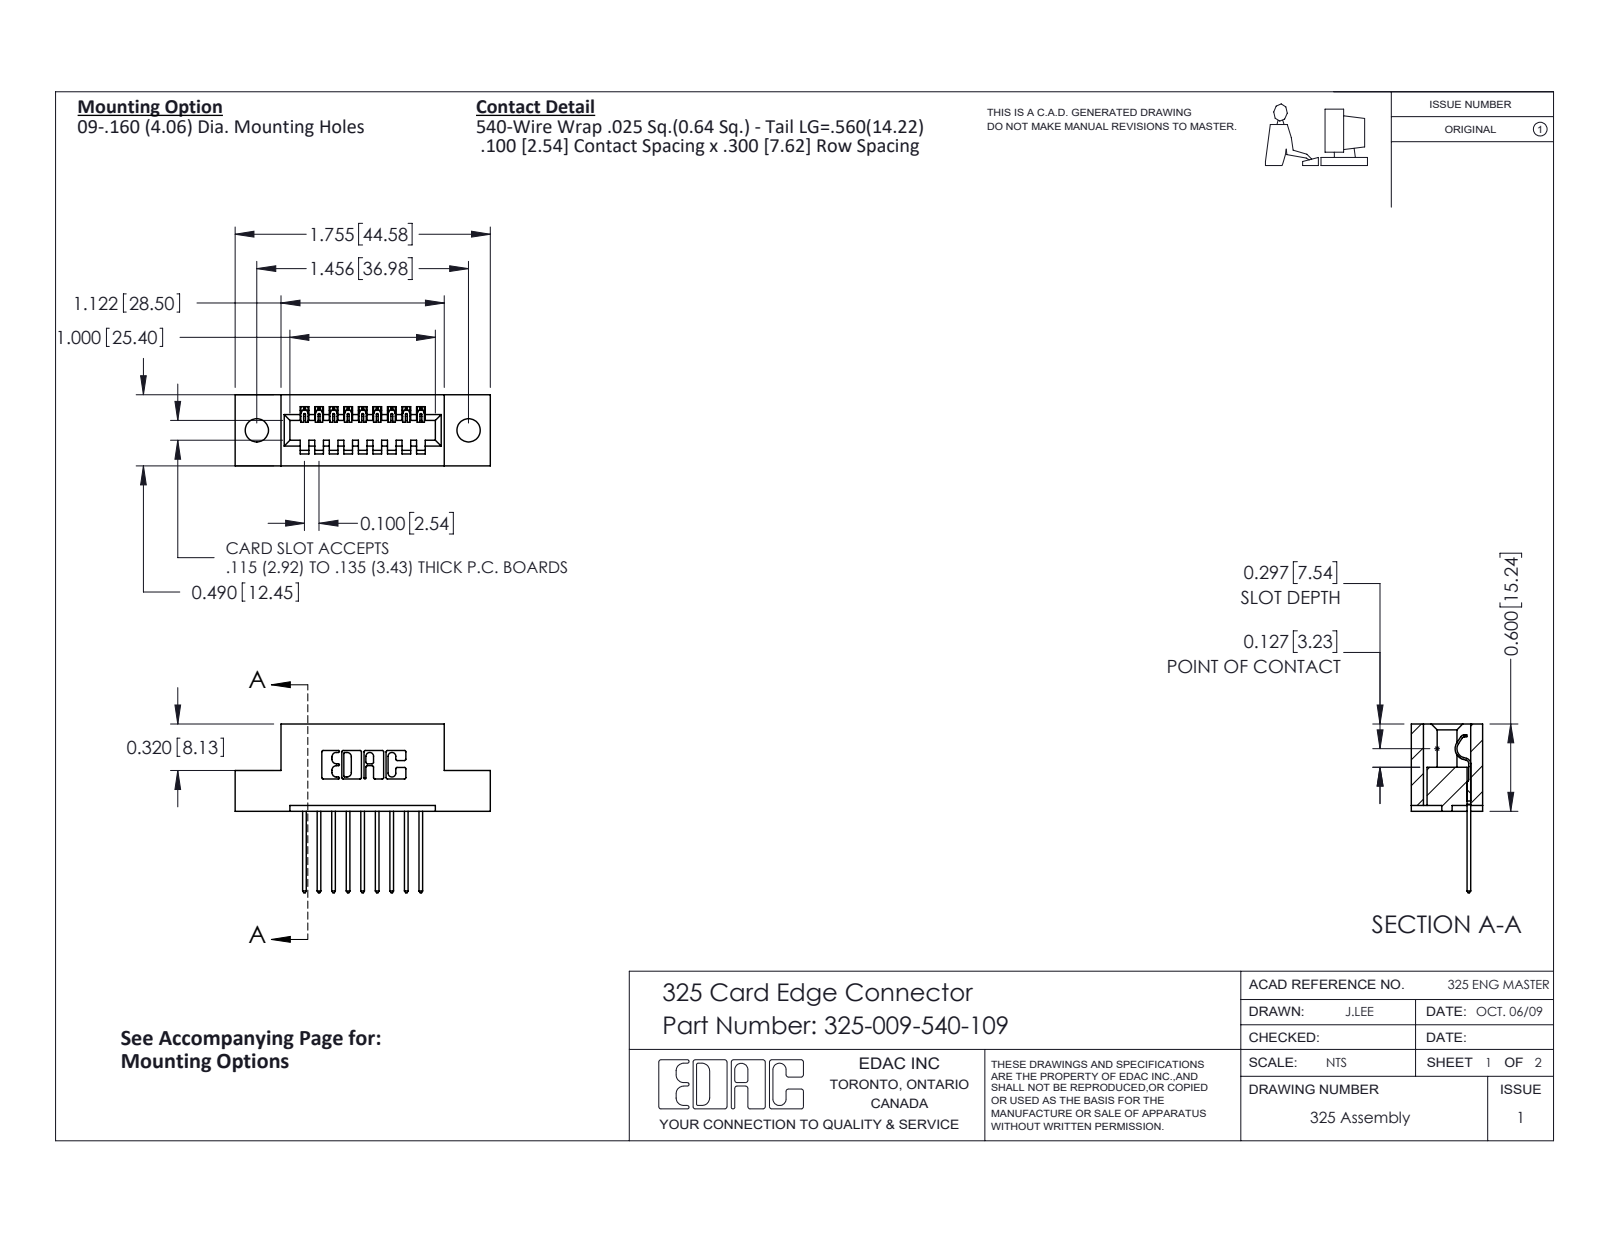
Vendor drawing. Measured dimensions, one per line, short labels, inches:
name: 325-009-540-109; 325-292-001_325-293-140; 325 Part_.160 TH
written by: SolidWorks 2016 (CONFIG_CONTROL_DESIGN)
unit: in
bodies: 10 solids, 636 faces (448 planar, 188 cylindrical, 0 other)
size: 1.755 × 1.16 × 0.49
volume: 0.316 in³; area: 7.884 in²
holes: 2× ⌀0.16
rounds: 22× R0.01, 18× R0.006, 18× R0.01, 6× R0.007, 6× R0.031, 3× R0.026, 1× R0.014, 1× R0.022
face distances: 0.3, 0.04, 0.083, 0.407, 0.1, 0.49, 0.2, 0.6, 0.4, 0.107
hole spacings: 1.456
